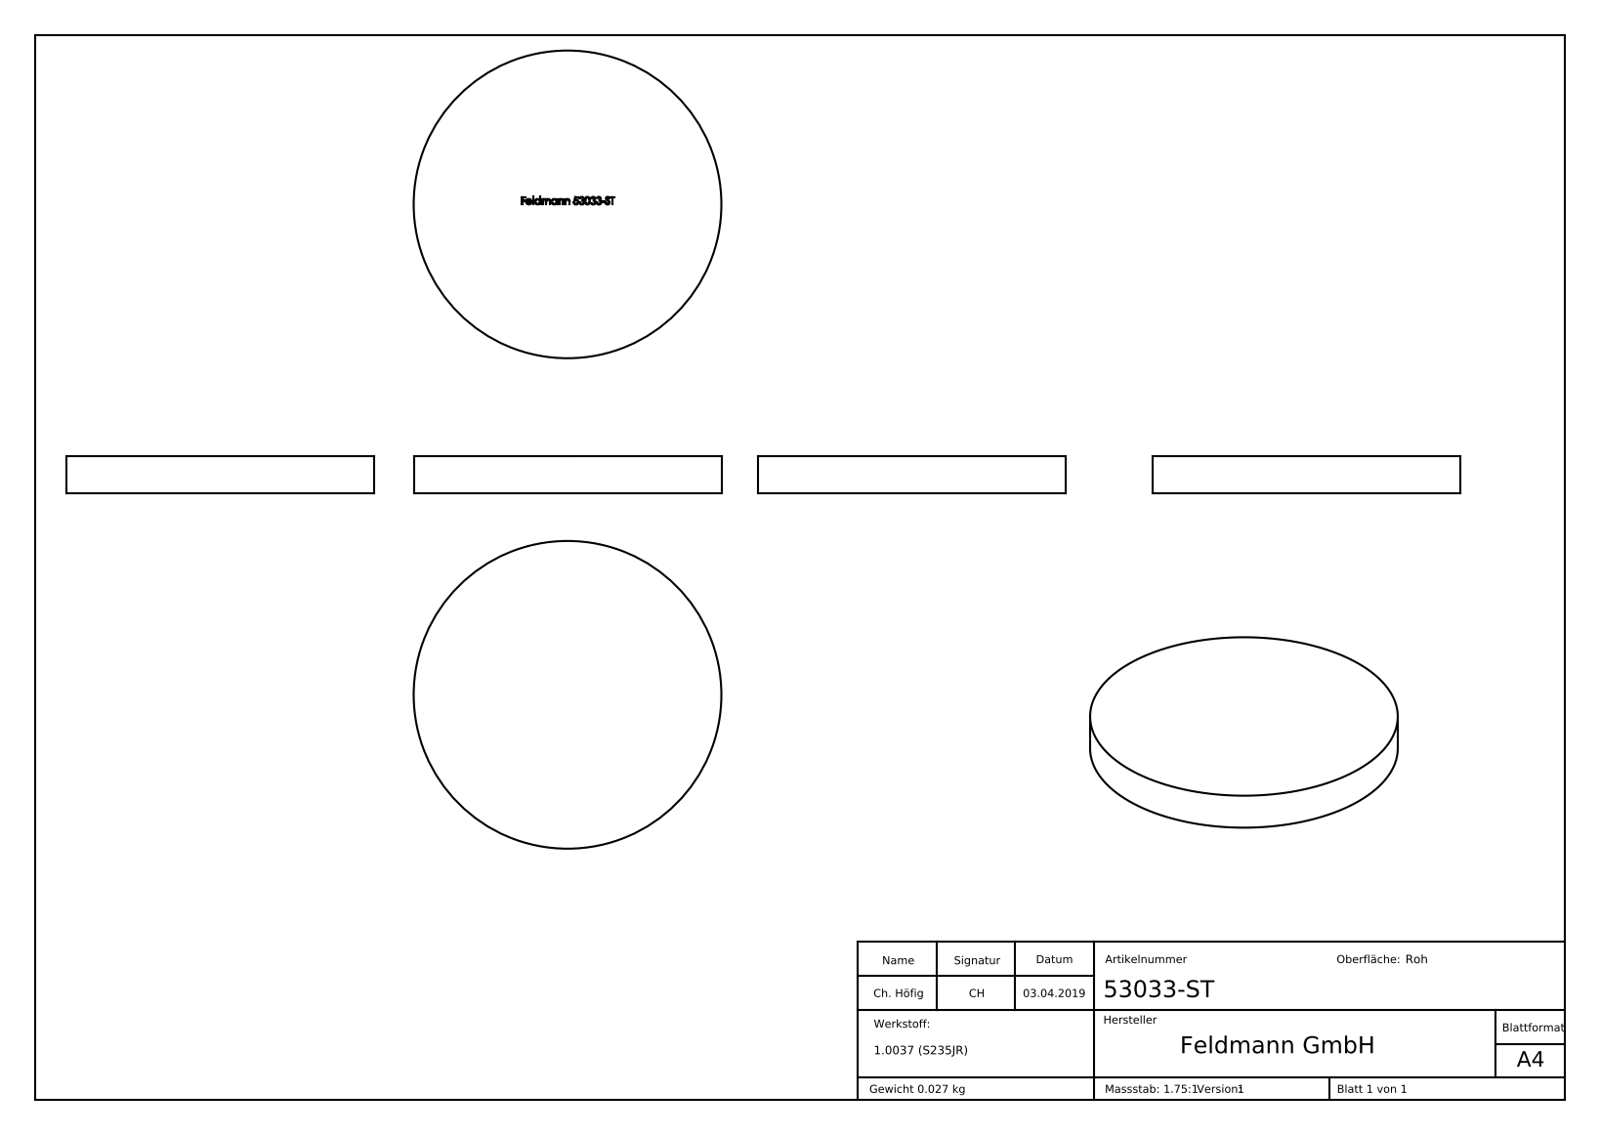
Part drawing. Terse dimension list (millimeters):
name: 53033-ST
written by: SolidWorks 2015 (CONFIG_CONTROL_DESIGN)
unit: mm
bodies: 1 solid, 229 faces (105 planar, 2 cylindrical, 122 other)
size: 33 × 33 × 4
volume: 3 421 mm³; area: 2 131 mm²
bosses: 1× ⌀33
face distances: 4, 3.9, 0.44, 0.99, 1.78, 0.67, 0.79, 1.21, 8.49, 9.7
